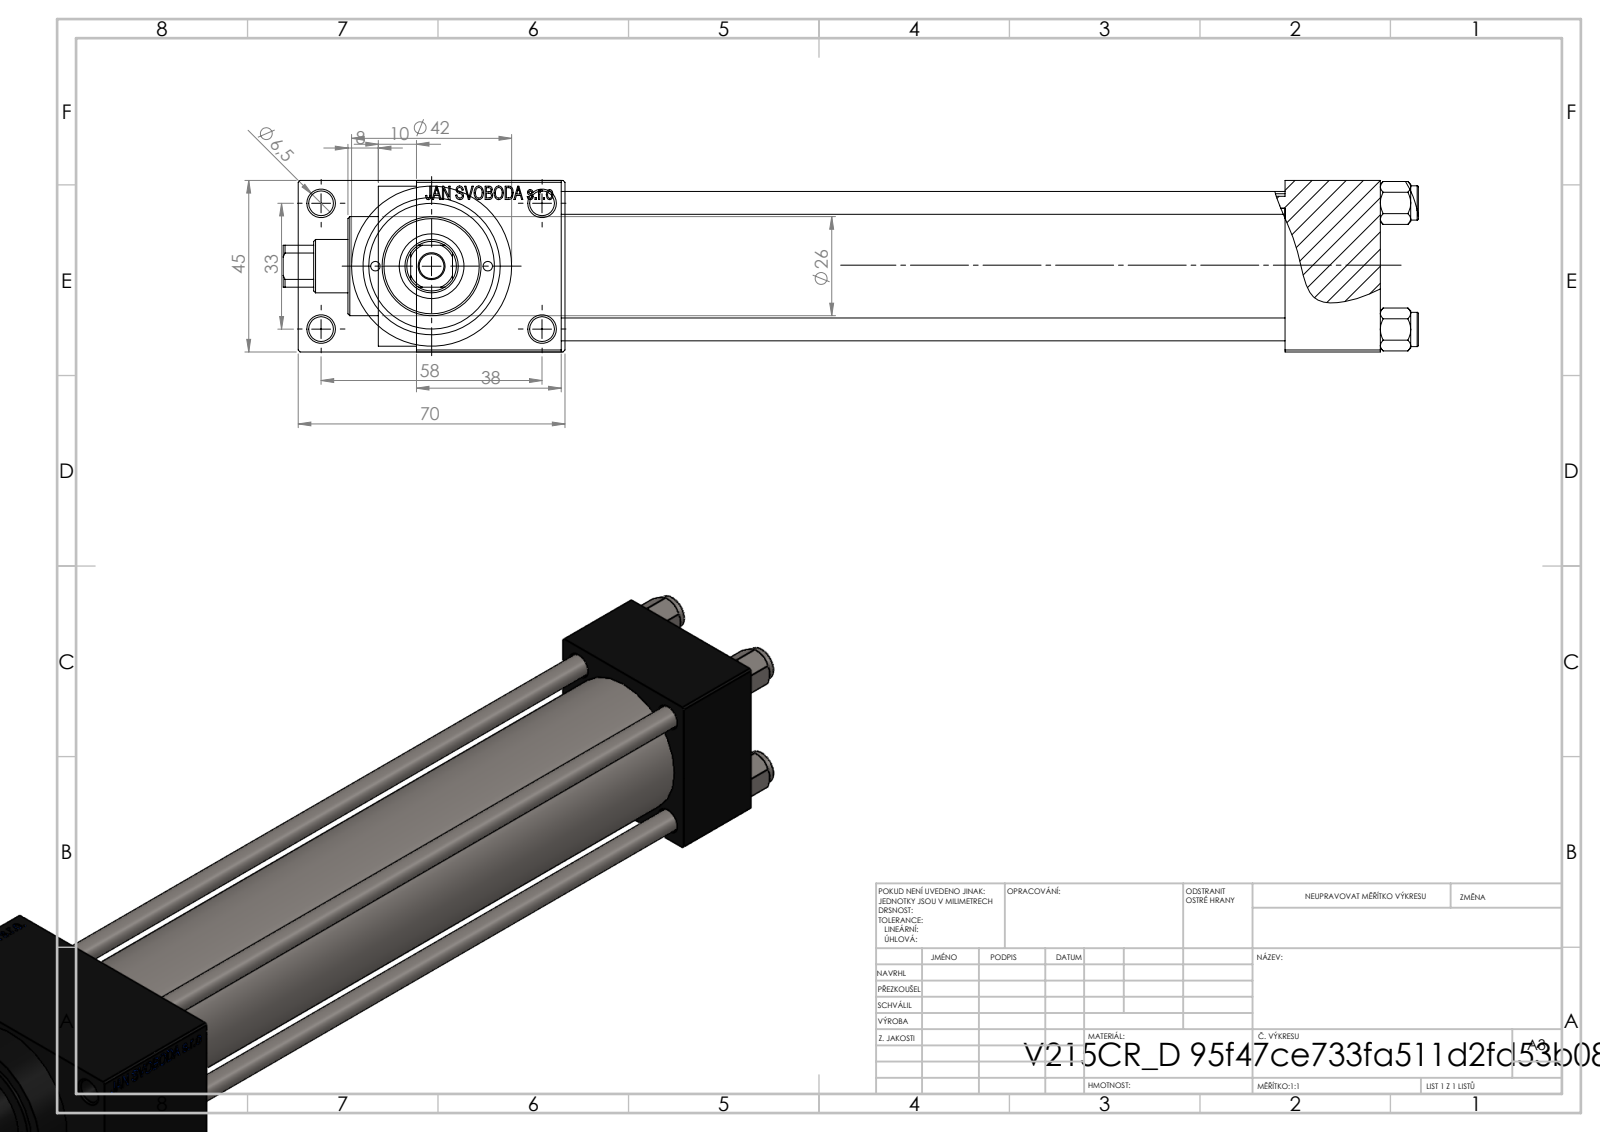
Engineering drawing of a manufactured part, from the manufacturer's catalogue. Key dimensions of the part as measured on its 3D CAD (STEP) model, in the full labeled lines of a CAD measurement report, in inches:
Part name (STEP PRODUCT): NUT_M5_D; V215CR_D_TYCINKA; V215CR_VCP_D; V215_VC_A (+1 more)
STEP written by: SolidWorks 2019 (CONFIG_CONTROL_DESIGN)
Units: inches
Bodies: 11 solids, 1110 faces (498 planar, 92 cylindrical, 520 other)
Overall size (bounding box): 11.732 × 2.756 × 1.772
Volume: 19.14 in³ · Surface area: 190.5 in²
Round holes (diameter × count): ⌀0.256 ×5, ⌀0.236 ×4, ⌀0.098 ×2, ⌀0.276 ×2, ⌀0.518 ×2, ⌀0.787 ×2, ⌀0.551 ×1, ⌀0.669 ×1, ⌀0.945 ×1, ⌀1.26 ×1, ⌀1.299 ×1
Round bosses / shafts (diameter × count): ⌀0.354 ×4, ⌀1.654 ×1, ⌀1.496 ×1, ⌀1.024 ×1
Partial cylindrical surfaces — rounded edges, fillets, slot ends (radius × count): R0.256 ×1
Main face-to-face distances: 1.772, 0.984, 0.492, 7.48, 8.465, 2.264, 8.976, 1.496, 9.961, 2.756
Hole centre spacings: 0.488, 0.657, 0.858, 0.924, 1.307, 1.314, 1.392, 1.396
